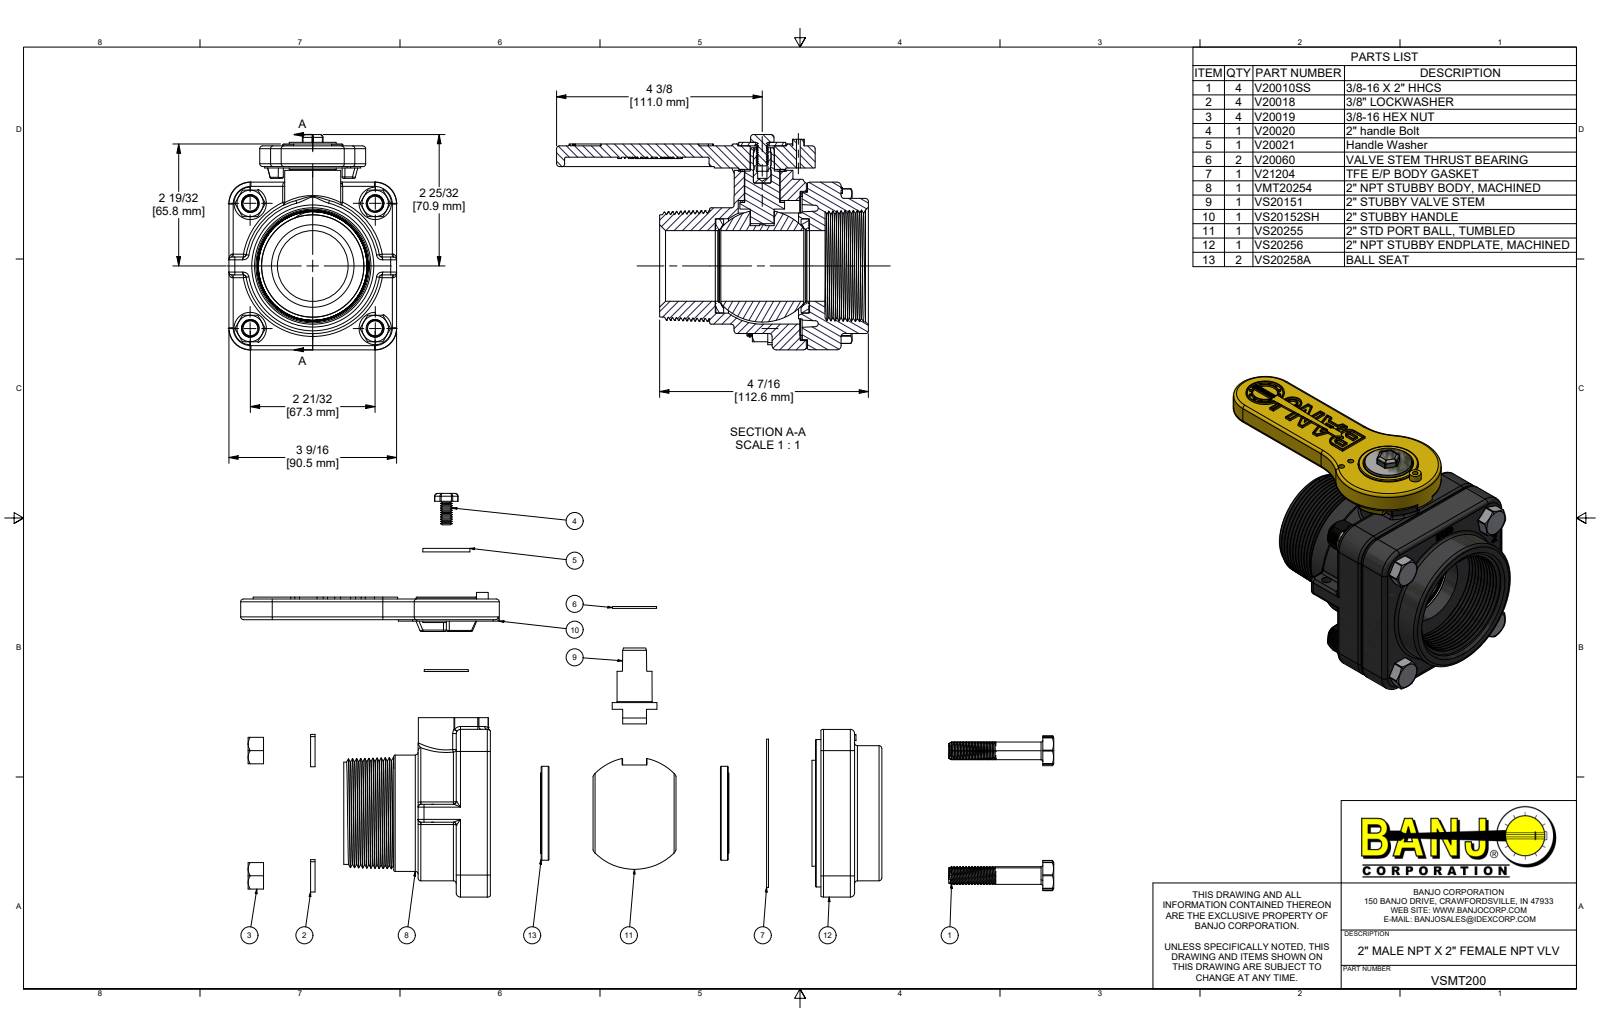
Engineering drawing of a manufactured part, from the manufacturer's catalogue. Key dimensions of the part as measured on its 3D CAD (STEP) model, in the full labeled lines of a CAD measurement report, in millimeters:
Part name (STEP PRODUCT): VSMT200; VMT20254; VXMT20254; V20010SS (+8 more)
STEP written by: Autodesk Inventor 2022 (AUTOMOTIVE_DESIGN)
Units: millimetres
Bodies: 25 solids, 2268 faces (855 planar, 567 cylindrical, 846 other)
Overall size (bounding box): 168.2 × 116.1 × 90.5
Volume: 439 000 mm³ · Surface area: 151 400 mm²
Round holes (diameter × count): ⌀9.5 ×5, ⌀7.8 ×4, ⌀9.8 ×4, ⌀10.3 ×4, ⌀10.7 ×4, ⌀3.3 ×2, ⌀5.1 ×2, ⌀3 ×1, ⌀5 ×1, ⌀7.1 ×1, ⌀8.9 ×1, ⌀13.8 ×1
Round bosses / shafts (diameter × count): ⌀8.2 ×60, ⌀17.4 ×4, ⌀9.5 ×4, ⌀80 ×1, ⌀79.5 ×1, ⌀72.9 ×1, ⌀57.2 ×1, ⌀51.8 ×1
Partial cylindrical surfaces — rounded edges, fillets, slot ends (radius × count): R1.5 ×32, R2.3 ×16, R0.8 ×14, R4.1 ×8, R3.2 ×4, R8.1 ×4, R11.4 ×4, R11.9 ×4
Main face-to-face distances: 90.4, 37.2, 1, 18.1, 19.1, 18.7, 0.6, 18.4, 2.9, 21
Hole centre spacings: 67.4, 47.5, 47.8, 67.3, 67.5, 95.3, 40.6, 95.1
